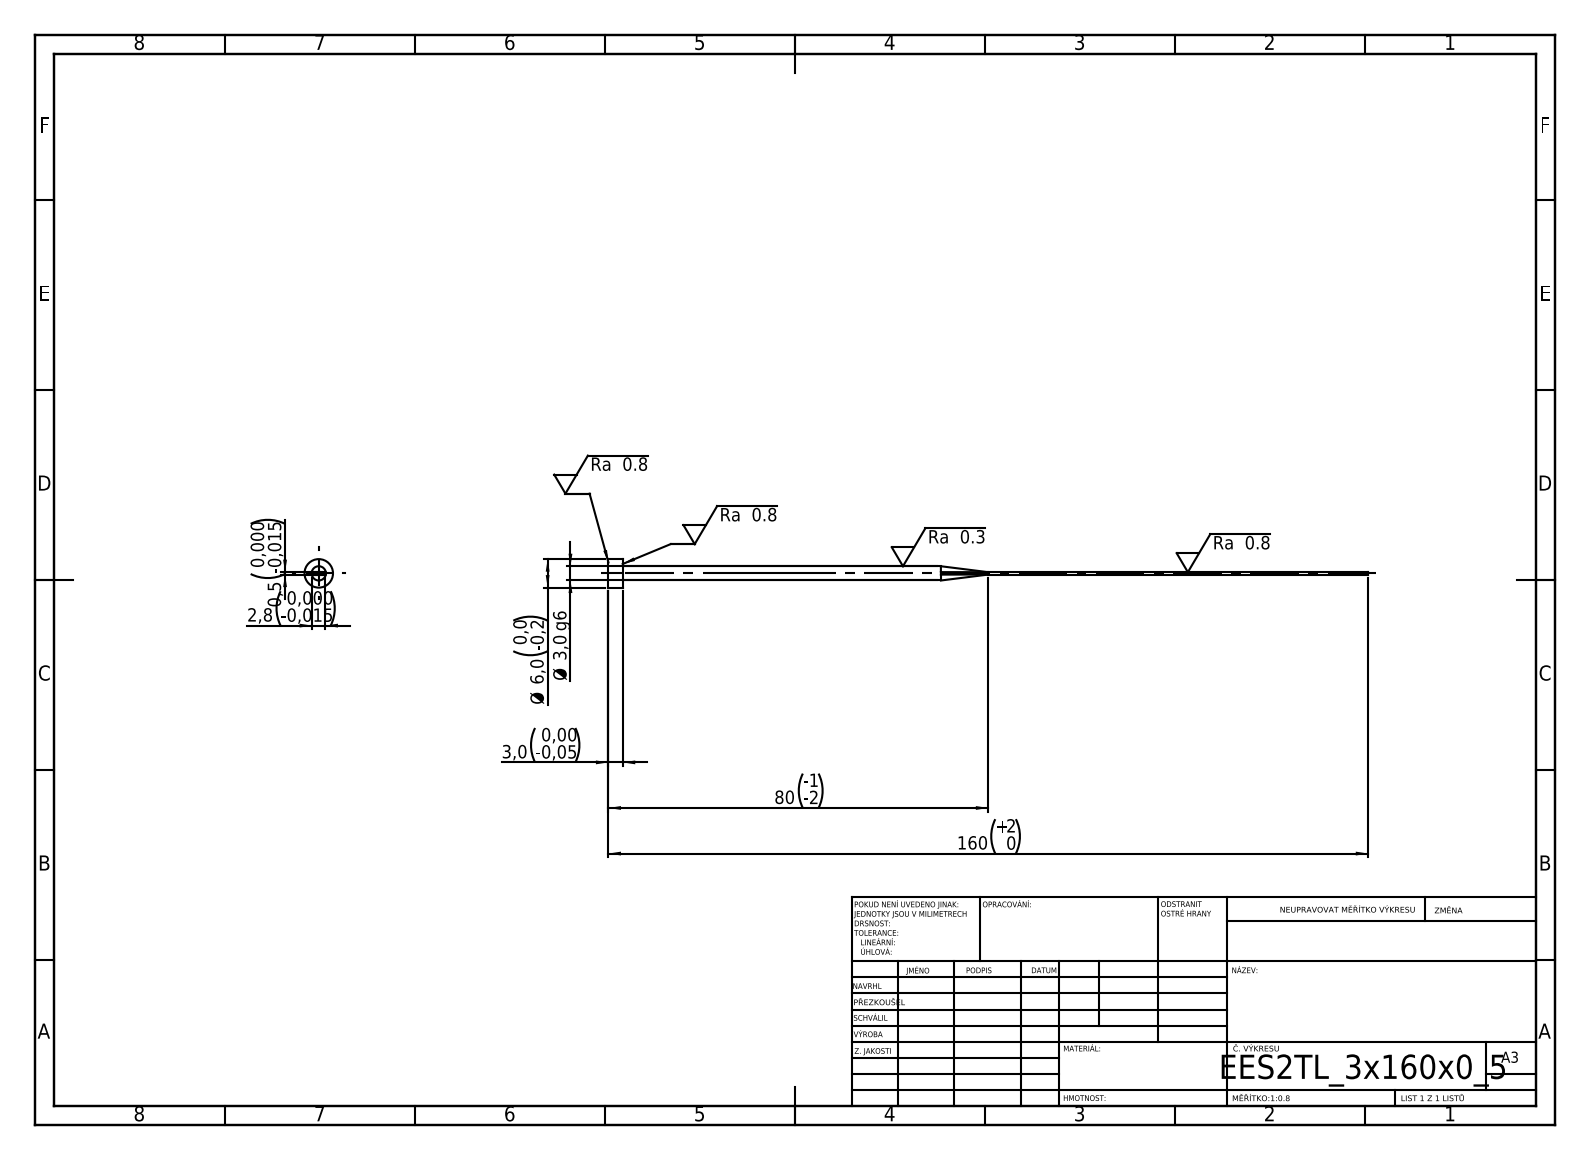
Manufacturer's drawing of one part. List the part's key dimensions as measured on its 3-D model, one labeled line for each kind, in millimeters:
STEP written by: SolidWorks 2019 (CONFIG_CONTROL_DESIGN)
Units: millimetres
Bodies: 1 solid, 15 faces (7 planar, 4 cylindrical, 4 other)
Overall size (bounding box): 160 × 6 × 6
Volume: 710 mm³ · Surface area: 1 344 mm²
Round bosses / shafts (diameter × count): ⌀6 ×1, ⌀3 ×1
Main face-to-face distances: 0.5, 2.8, 3, 160, 157
